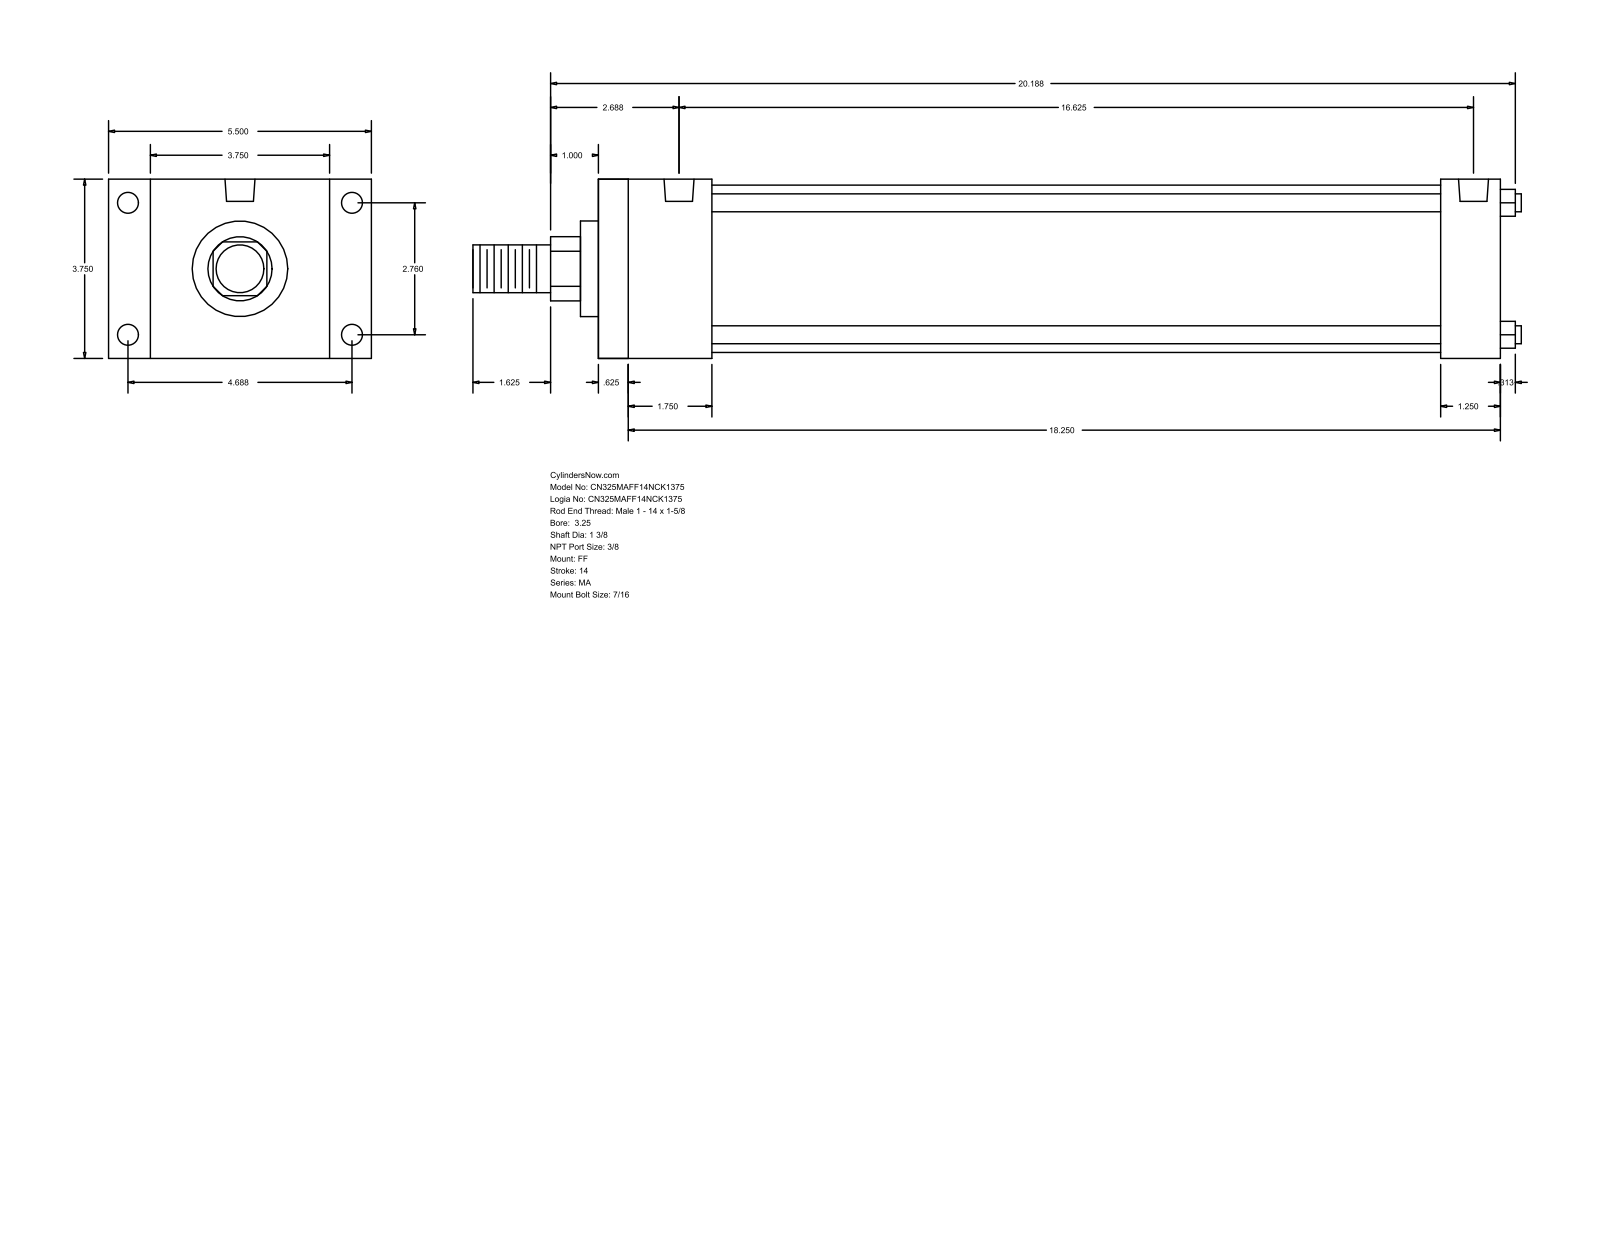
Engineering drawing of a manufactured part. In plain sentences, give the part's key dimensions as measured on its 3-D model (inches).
The part is named "MA_FF__0325_1.375". Its 3-D file was written by "GSSL Pune (CONFIG_CONTROL_DESIGN)". It is 0 solids with 92 faces: 64 planar, 28 cylindrical and 0 other. Overall it measures 21.937 by 5.5 by 3.75 inches. Round holes: 8 of diameter 0.437, 2 of diameter 0.627. Round bosses or shafts: 4 of diameter 0.375, 1 of diameter 3.5, 1 of diameter 2, 1 of diameter 1.375, 1 of diameter 1. Partial cylindrical surfaces (rounded edges, fillets, slot ends): 1 of radius 0.672. The main face-to-face distances are 3.75, 18.875, 0.625, 18.25, 0.875, 4.625, 2.375, 17.625, 1.75, 17. The hole center spacings are 0.188, 2.76, 4.687, 5.439, 16.25, 16.437, 16.625.
